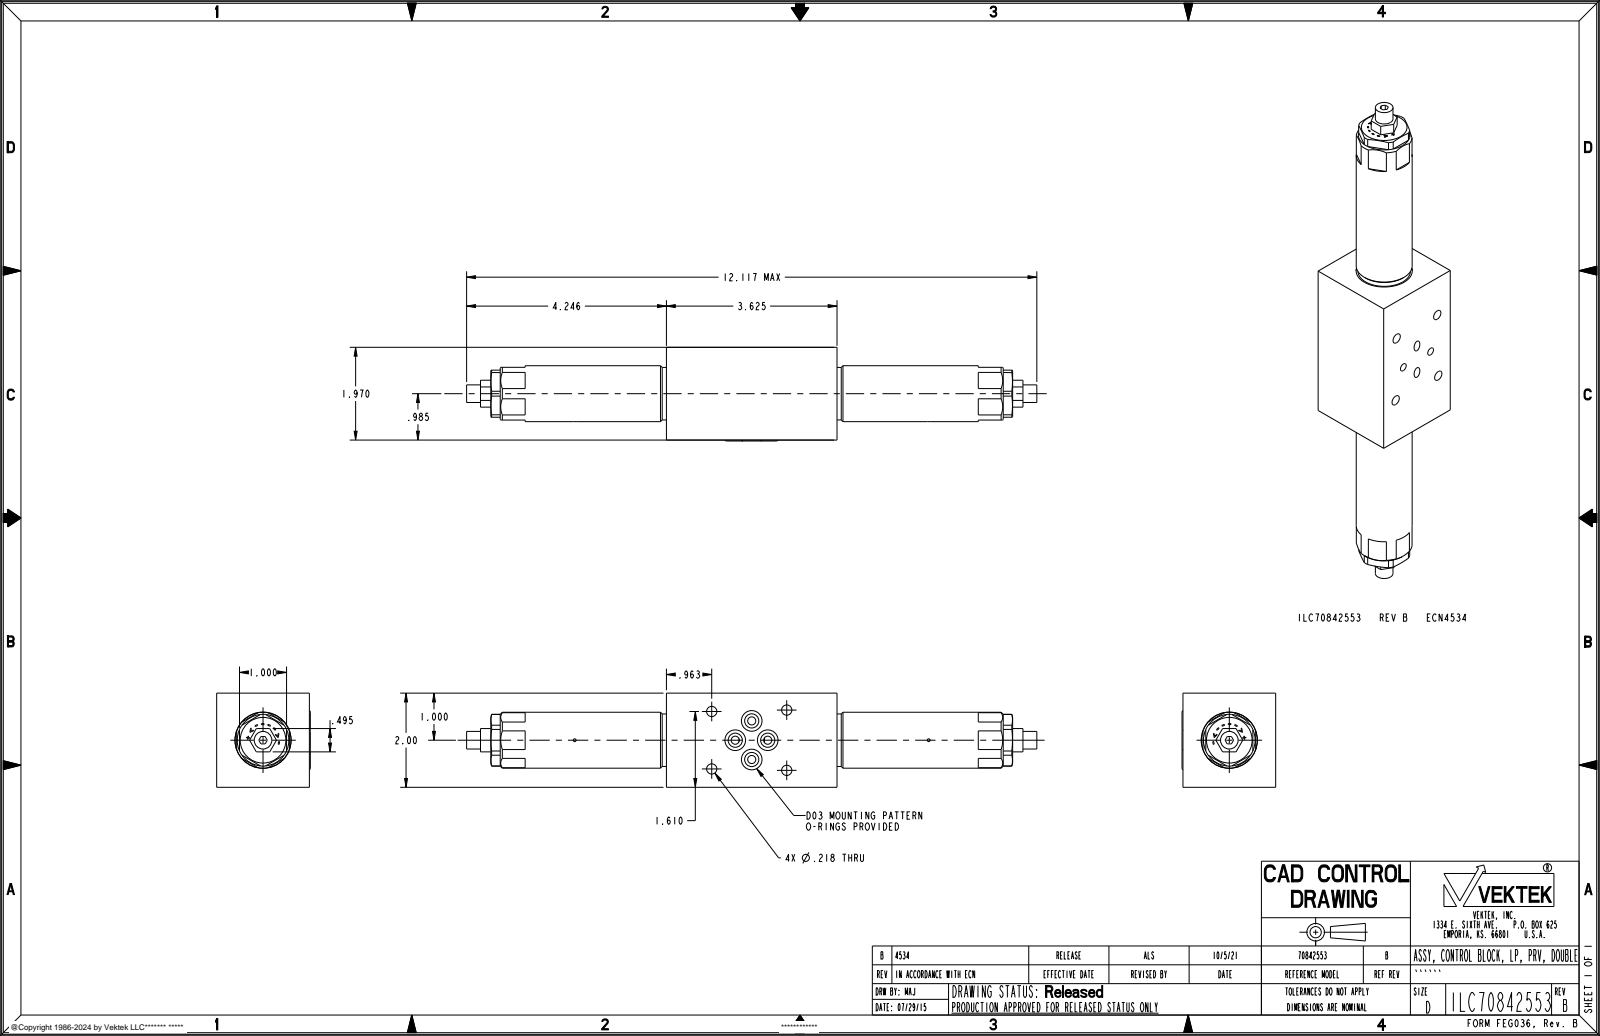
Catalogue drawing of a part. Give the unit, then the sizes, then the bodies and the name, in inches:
Units: inches
Overall size (bounding box): 12.366 × 2 × 1.99
Round holes (diameter × count): ⌀0.172 ×5, ⌀0.218 ×4, ⌀0.438 ×4, ⌀0.06 ×2, ⌀0.158 ×1, ⌀0.172 ×1, ⌀0.563 ×1, ⌀0.625 ×1, ⌀0.626 ×1, ⌀0.688 ×1, ⌀0.72 ×1, ⌀0.812 ×1
Round bosses / shafts (diameter × count): ⌀1.188 ×1, ⌀1.115 ×1, ⌀0.8 ×1, ⌀0.374 ×1
Partial cylindrical surfaces — rounded edges, fillets, slot ends (radius × count): R0.03 ×12, R0.55 ×1
Main face-to-face distances: 2, 1.97, 3.625, 1.12, 3.953, 7.578, 0.575, 10.956, 3.378, 7.003
Hole centre spacings: 3.775, 0.533, 0.539, 0.757, 0.779, 0.789, 0.873, 1.268
Volume: 18.06 in³ · Surface area: 104.7 in²
Bodies: 1 solid, 490 faces (248 planar, 122 cylindrical, 120 other)
Part name (STEP PRODUCT): ILC70842553
STEP written by: PRO/ENGINEER BY PARAMETRIC TECHNOLOGY CORPORATION, 2013320 (AUTOMOTIVE_DESIGN)
